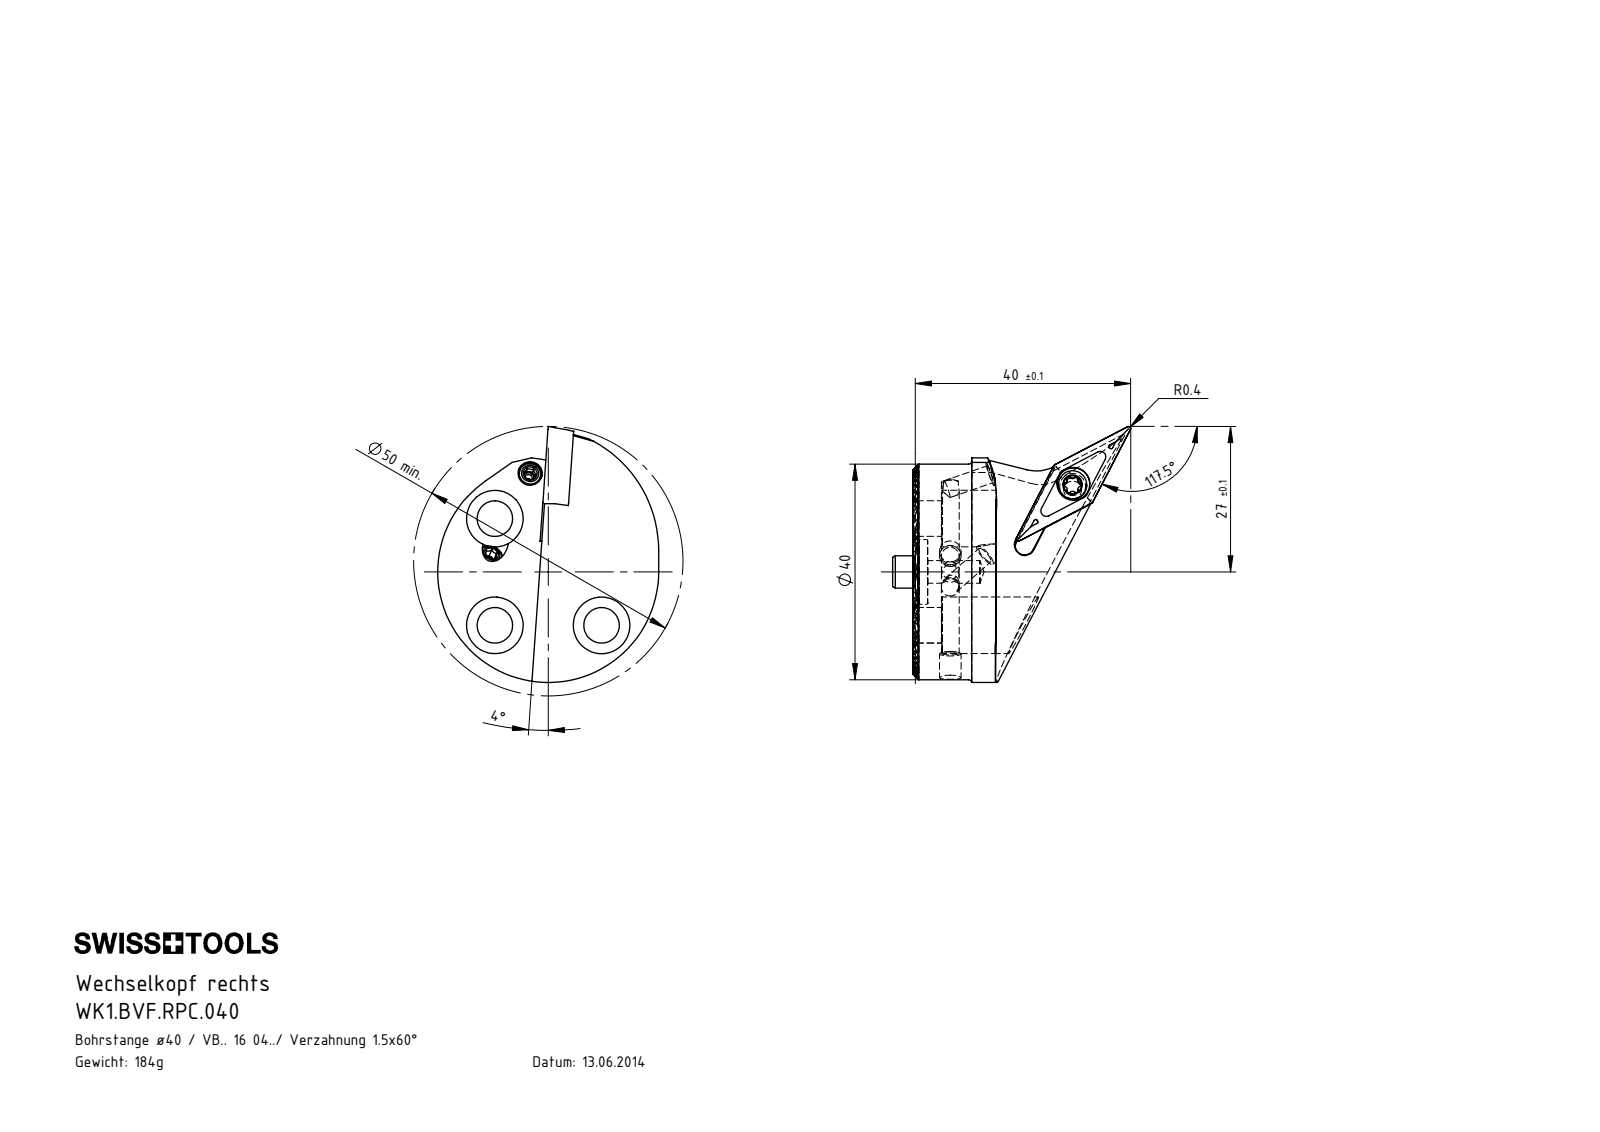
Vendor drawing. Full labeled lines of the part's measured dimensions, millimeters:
Part name (STEP PRODUCT): KVT_MB_600_040; WK1.BVF.RPC.040; WCB-ER2.001.009_A; WKX-ER1.004.005_A_PreviewCfg (+3 more)
STEP written by: SolidWorks 2017 (AUTOMOTIVE_DESIGN)
Units: millimetres
Bodies: 10 solids, 414 faces (221 planar, 106 cylindrical, 87 other)
Overall size (bounding box): 47.5 × 44.2 × 41
Volume: 22 948 mm³ · Surface area: 10 596 mm²
Round holes (diameter × count): ⌀3.3 ×5, ⌀4.2 ×3, ⌀6.6 ×3, ⌀10.5 ×3, ⌀1.7 ×2, ⌀3 ×2, ⌀4 ×2, ⌀4.4 ×1, ⌀6.1 ×1, ⌀12 ×1
Round bosses / shafts (diameter × count): ⌀4 ×5, ⌀40 ×1, ⌀6 ×1, ⌀5.25 ×1
Partial cylindrical surfaces — rounded edges, fillets, slot ends (radius × count): R0.12 ×26, R0.34 ×6, R0.59 ×6, R0.15 ×2, R1.75 ×1, R7 ×1, R20 ×1, R20.5 ×1
Main face-to-face distances: 1.3, 2.6, 3.9, 12.99, 5.2, 11.69, 9.09, 10.39, 7.79, 6.5
Hole centre spacings: 14, 19.8, 28
